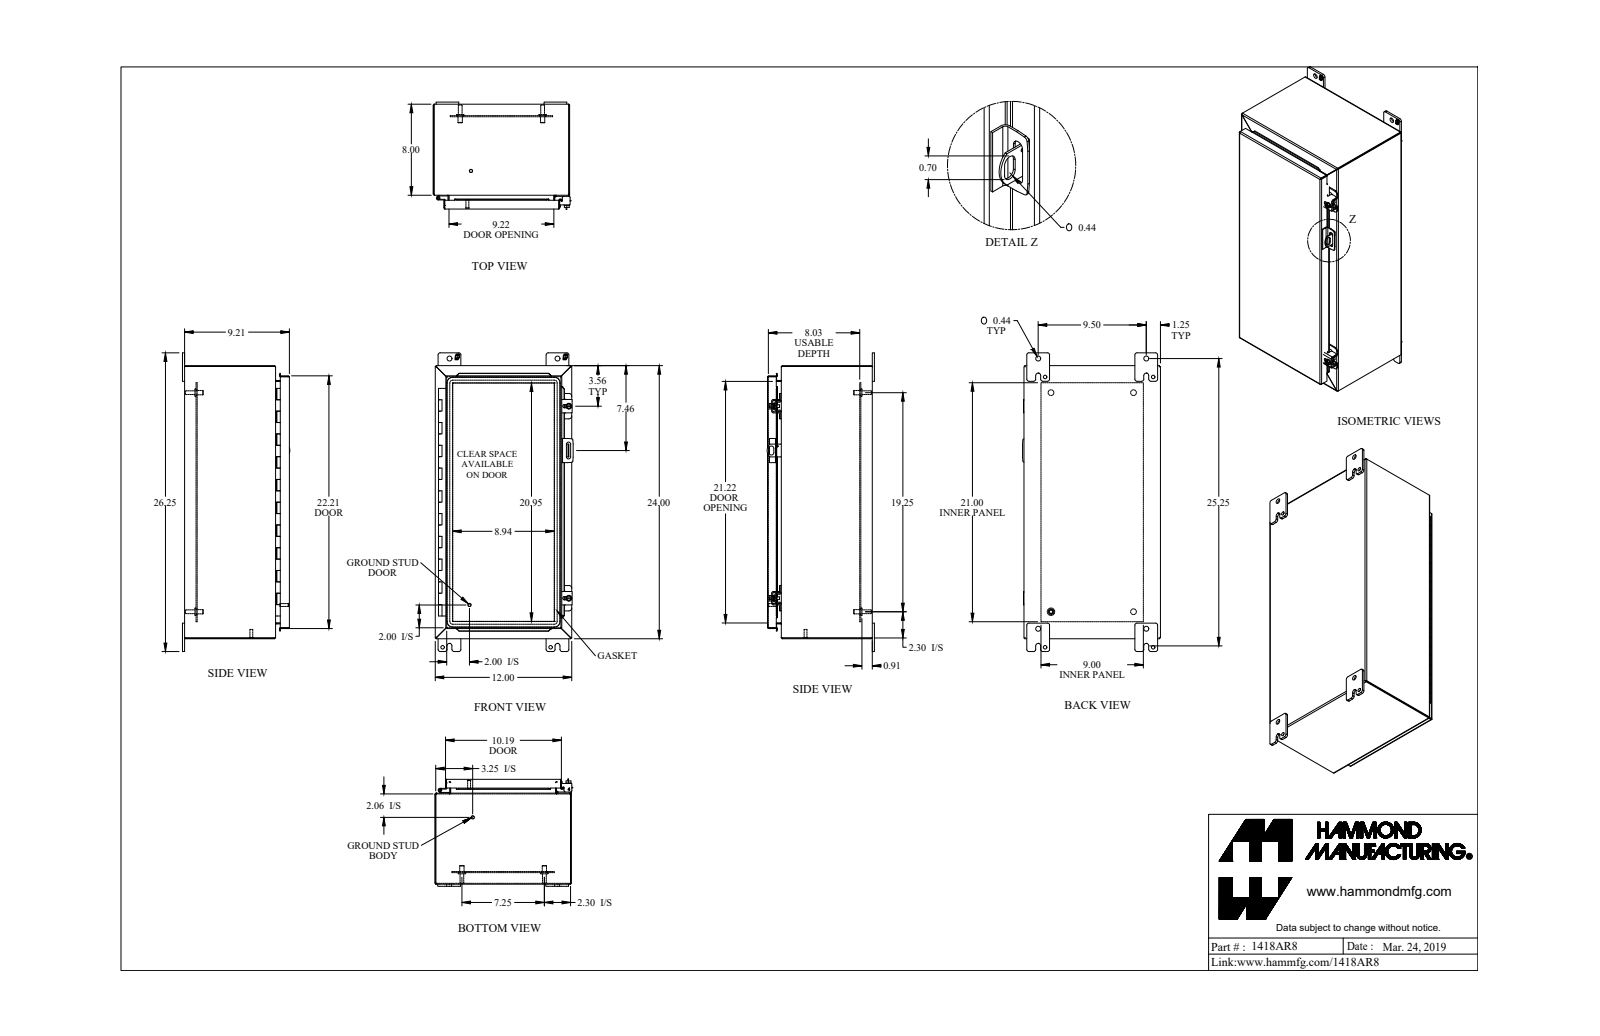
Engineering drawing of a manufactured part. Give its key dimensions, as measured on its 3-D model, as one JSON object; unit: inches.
{"part_name": "1418AR8", "step_written_by": "SolidWorks 2019 (AUTOMOTIVE_DESIGN)", "units": "inches", "bodies": {"solids": 37, "faces": 1001, "planar": 688, "cylindrical": 259, "other": 54}, "overall_size": [26.25, 12.125, 9.437], "volume_in3": 128.9, "surface_area_in2": 3366, "round_holes": [[0.313, 4], [0.437, 4], [0.5, 4], [0.213, 2], [0.265, 2], [0.307, 2], [0.375, 2], [0.445, 2], [0.125, 1], [0.187, 1]], "round_bosses_or_shafts": [[0.65, 4], [0.375, 4], [0.33, 4], [1, 2], [0.5, 2], [0.39, 2], [0.281, 2], [0.25, 2]], "partial_cylinders_radius": [[0.188, 26], [0.036, 20], [0.108, 20], [0.048, 13], [0.143, 13], [0.007, 8], [0.045, 8], [0.079, 8]], "face_to_face_distances": [0.072, 9.113, 11.928, 9.041, 0.937, 9.185, 1.009, 0.095, 8.081, 8.009], "hole_center_spacings": [20.57, 1.735, 9.5, 19.25, 23.75, 25.58, 2.434, 3.204]}
